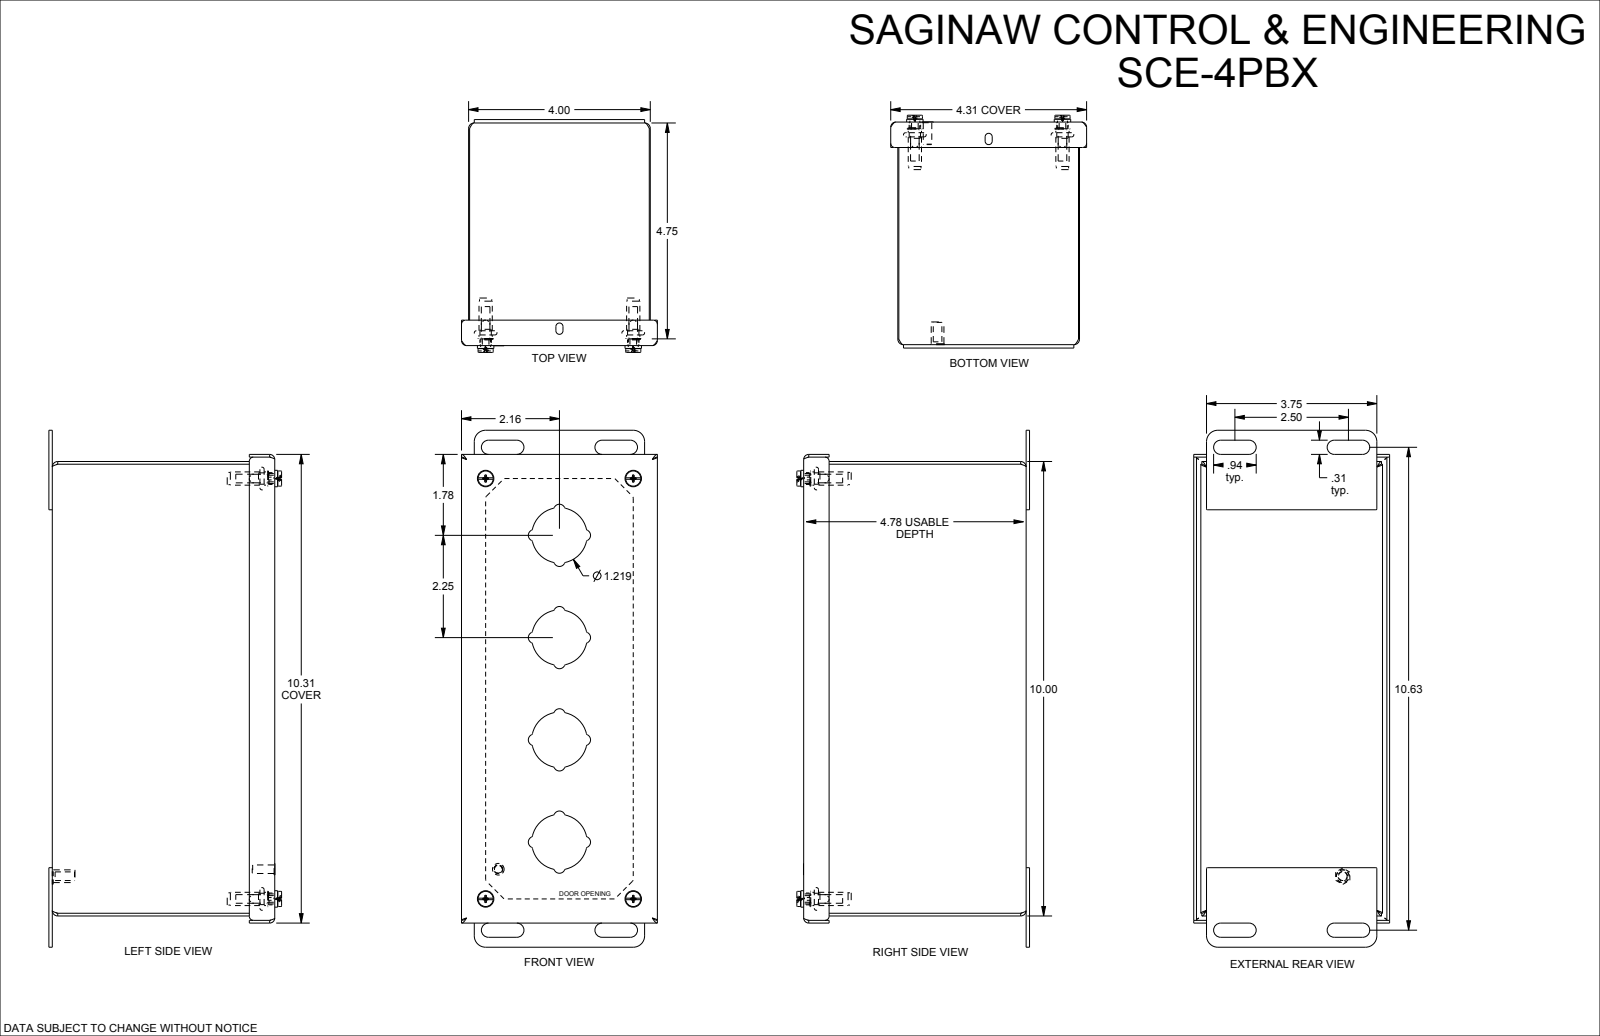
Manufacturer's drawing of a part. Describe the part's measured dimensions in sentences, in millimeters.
The part is named "SCE-4PBX-RAL1018". Its 3-D file was written by "SolidWorks 2021 (AUTOMOTIVE_DESIGN)". It is 19 solids with 583 faces: 209 planar, 212 cylindrical and 162 other. Overall it measures 288.9 by 130.1 by 109.5 millimeters. Its volume is 256 300 cubic millimeters and its surface area 335 700 square millimeters. Round holes: 5 of diameter 4.8, 4 of diameter 5.6, 4 of diameter 6.4, 4 of diameter 6.4, 4 of diameter 8.1. Round bosses or shafts: 5 of diameter 4.8, 4 of diameter 11.1, 4 of diameter 9.2, 4 of diameter 8.6, 4 of diameter 8.5, 4 of diameter 7.4, 4 of diameter 6.9, 4 of diameter 6.6. Partial cylindrical surfaces (rounded edges, fillets, slot ends): 32 of radius 1, 16 of radius 3.2, 12 of radius 1.5, 8 of radius 0.4, 8 of radius 1.6, 8 of radius 2.9, 8 of radius 4, 8 of radius 6.2. The main face-to-face distances are 1.5, 100.1, 122.9, 98.6, 101.6, 121.4, 124.4, 252.5, 254, 251. The hole center spacings are 235, 249, 82.6, 234.9, 82.5, 82.6, 248.9, 71.
